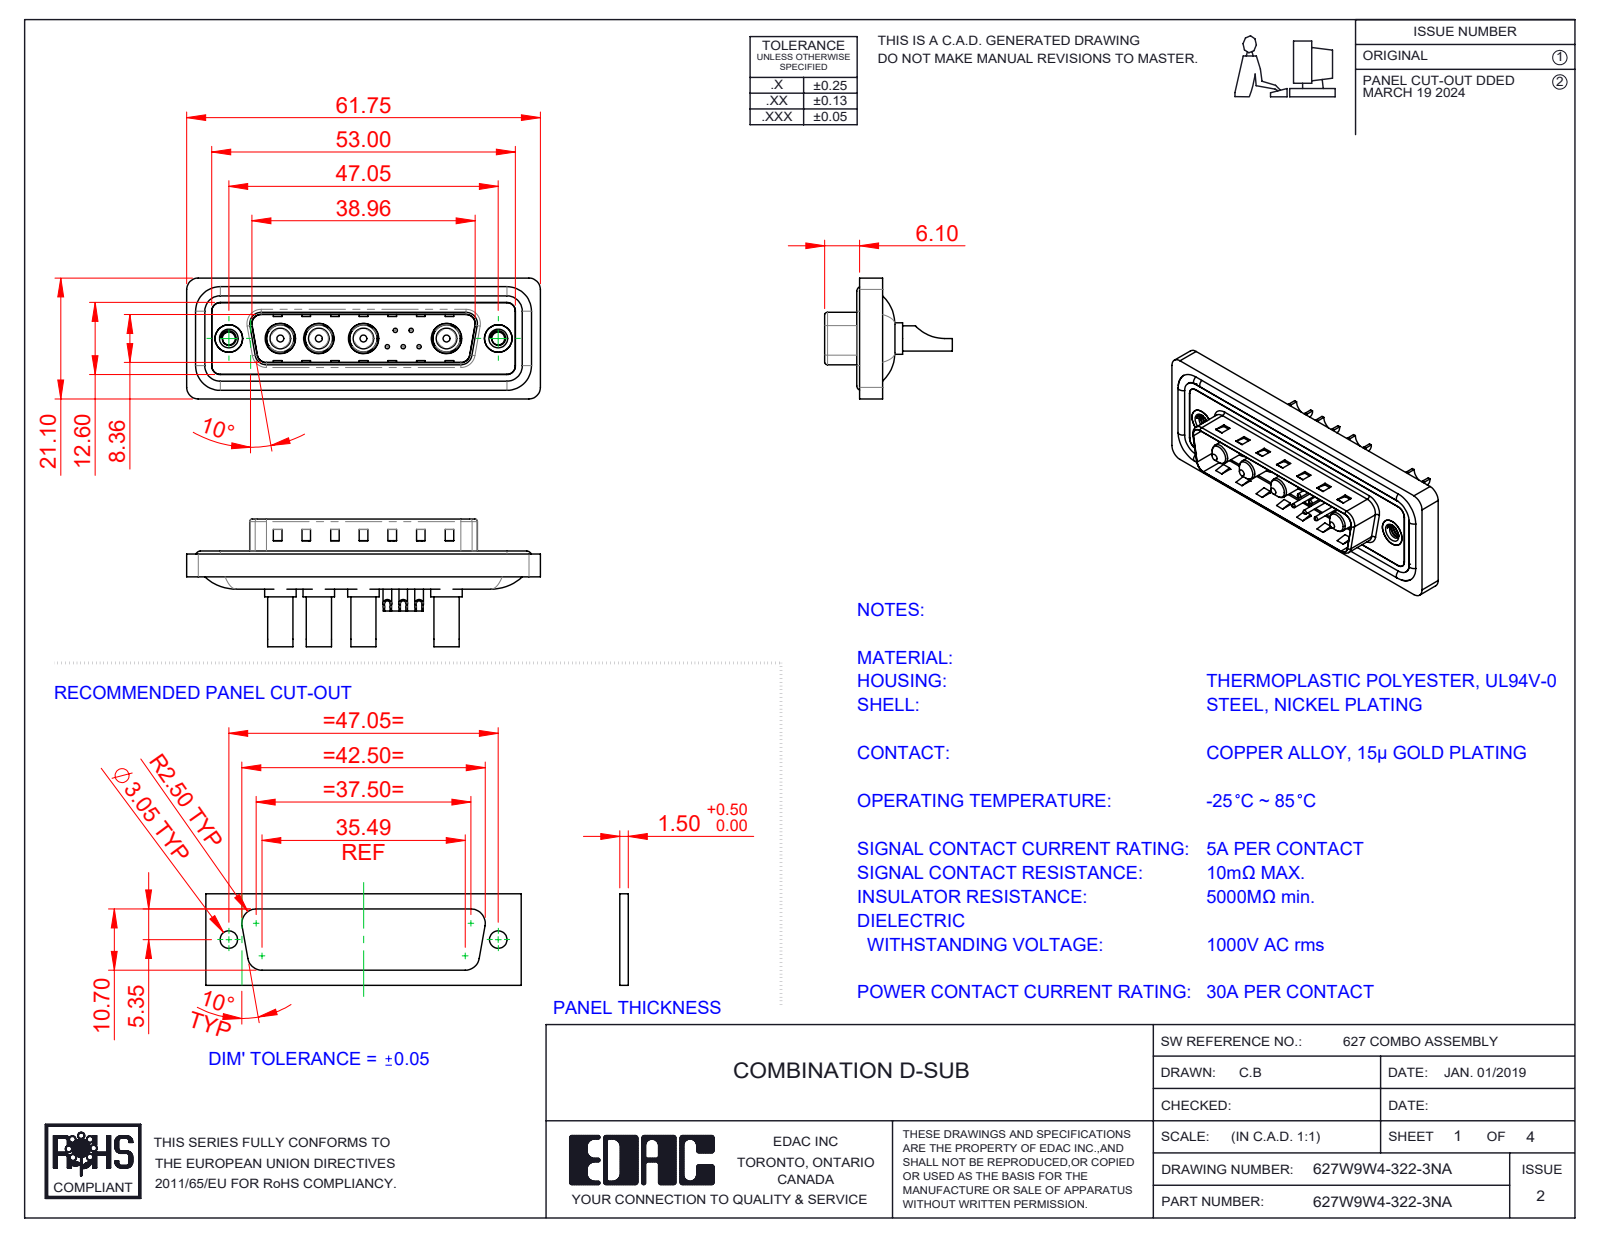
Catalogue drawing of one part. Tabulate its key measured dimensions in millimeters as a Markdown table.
| quantity | value |
| --- | --- |
| part name | 627Combo Shell Front_25 Contacts; 627W9W4-322-3NA; 627Combo Threaded Rivet_A; 627Combo Housing_9W4 (+5 more) |
| STEP written by | SolidWorks 2023 (CONFIG_CONTROL_DESIGN) |
| units | millimeters |
| bodies | 20 solids, 846 faces (306 planar, 358 cylindrical, 182 other) |
| overall size | 61.75 × 22.3 × 21.1 |
| volume | 7 509 mm³ |
| surface area | 12 303 mm² |
| round holes (diameter × count) | 0.75 × 5, 1 × 5, 1.6 × 5, 2 × 5, 3.5 × 4, 4.85 × 4, 5.3 × 4, 2.26 × 2, 4 × 2, 4.8 × 2, 5 × 2 |
| round bosses / shafts (diameter × count) | 1.5 × 5, 5.5 × 4, 5.2 × 4, 4.75 × 4, 4.4 × 4, 3.75 × 4, 3.6 × 4, 1.6 × 4 |
| partial cylindrical surfaces (radius × count) | 1.5 × 22, 2 × 18, 0.5 × 8, 1.6 × 8, 1 × 6, 0.25 × 4, 0.6 × 4, 0.65 × 4 |
| main face-to-face distances | 0.4, 1.5, 1.1, 0.5, 1.6, 3.1, 2.9, 0.82, 9.58, 5.65 |
| hole center spacings | 3.16, 2.77, 5.04, 14.51, 2.78, 4.4, 4.41, 5 |
